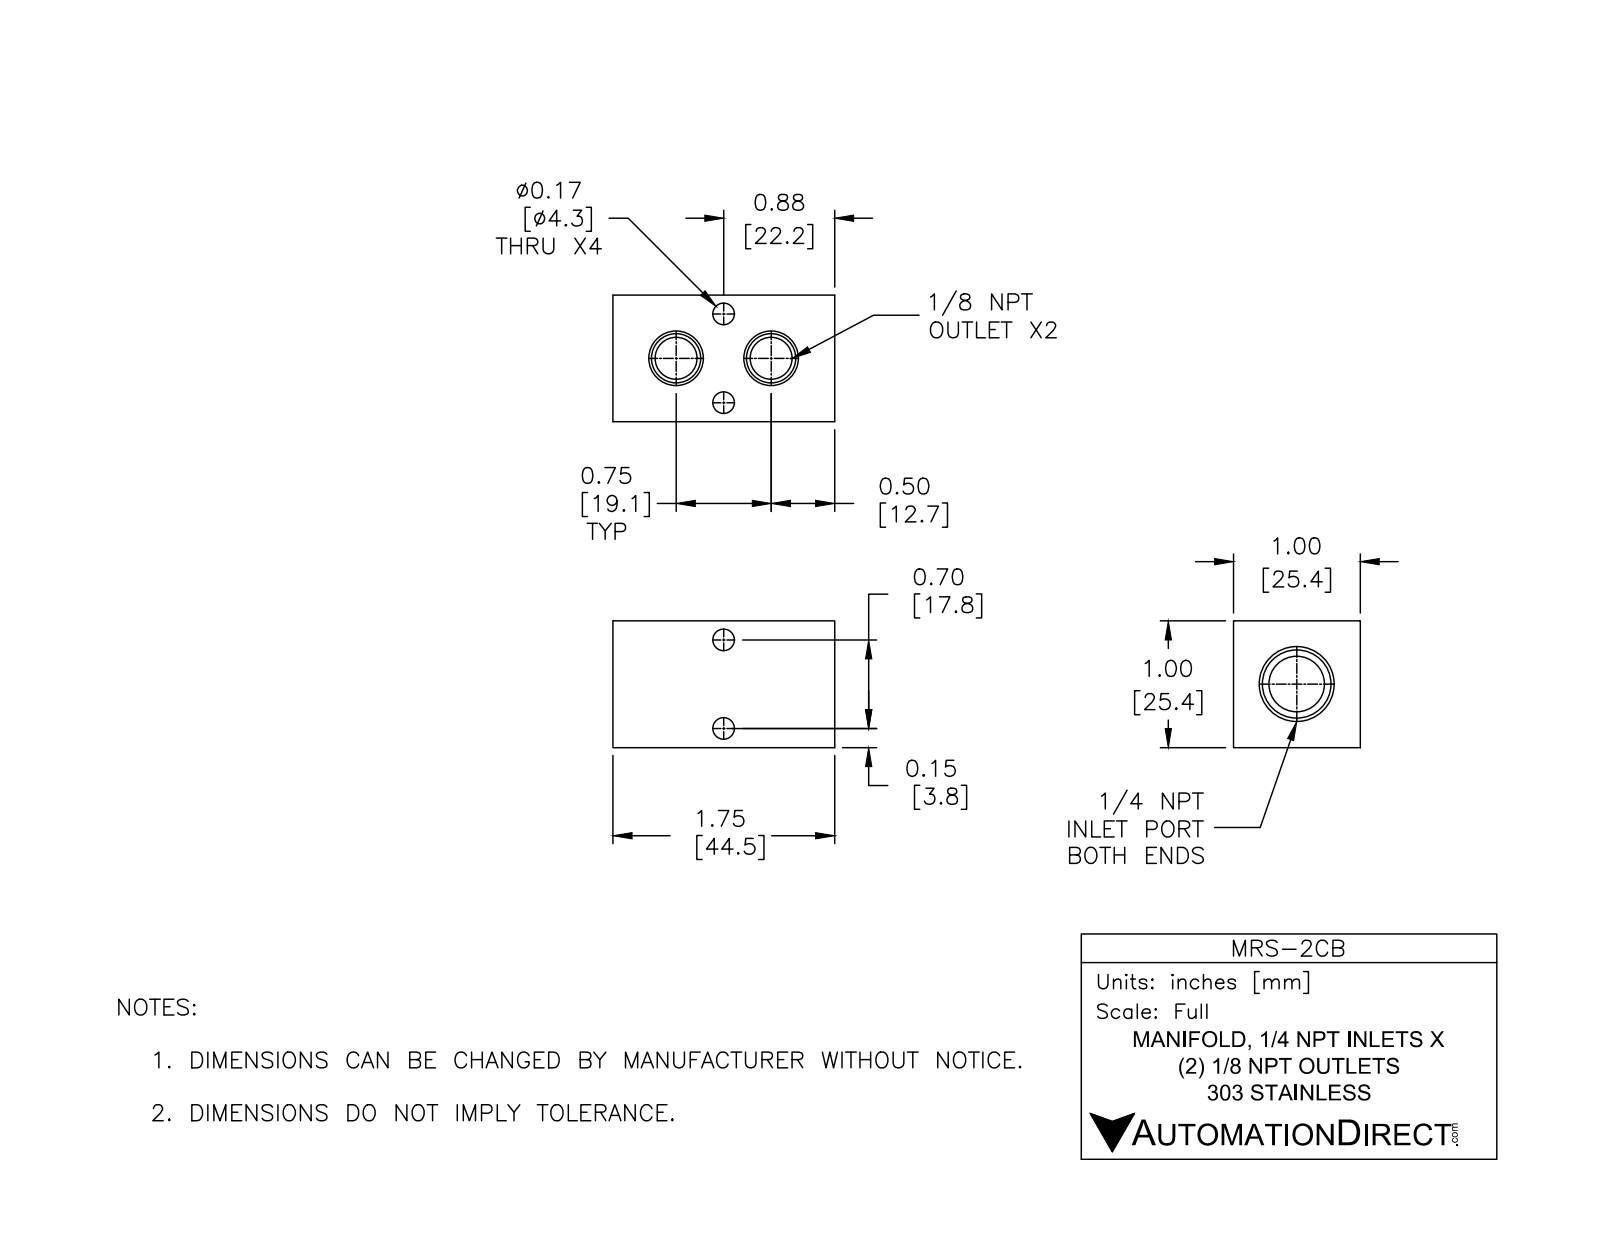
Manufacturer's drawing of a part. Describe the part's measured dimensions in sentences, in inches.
The part is named "MRS-2CB". Its 3-D file was written by "SolidWorks 2015 (CONFIG_CONTROL_DESIGN)". It is 1 solid with 55 faces: 10 planar, 29 cylindrical and 16 other. Overall it measures 1.75 by 1 by 1 inches. Its volume is 1.282 cubic inches and its surface area 13.04 square inches. Round holes: 4 of diameter 0.17, 1 of diameter 0.438. Partial cylindrical surfaces (rounded edges, fillets, slot ends): 2 of radius 0.166. The main face-to-face distances are 1, 1.75, 0.39, 1.36, 0.73, 0.27, 0.97. The hole center spacings are 0.7.
